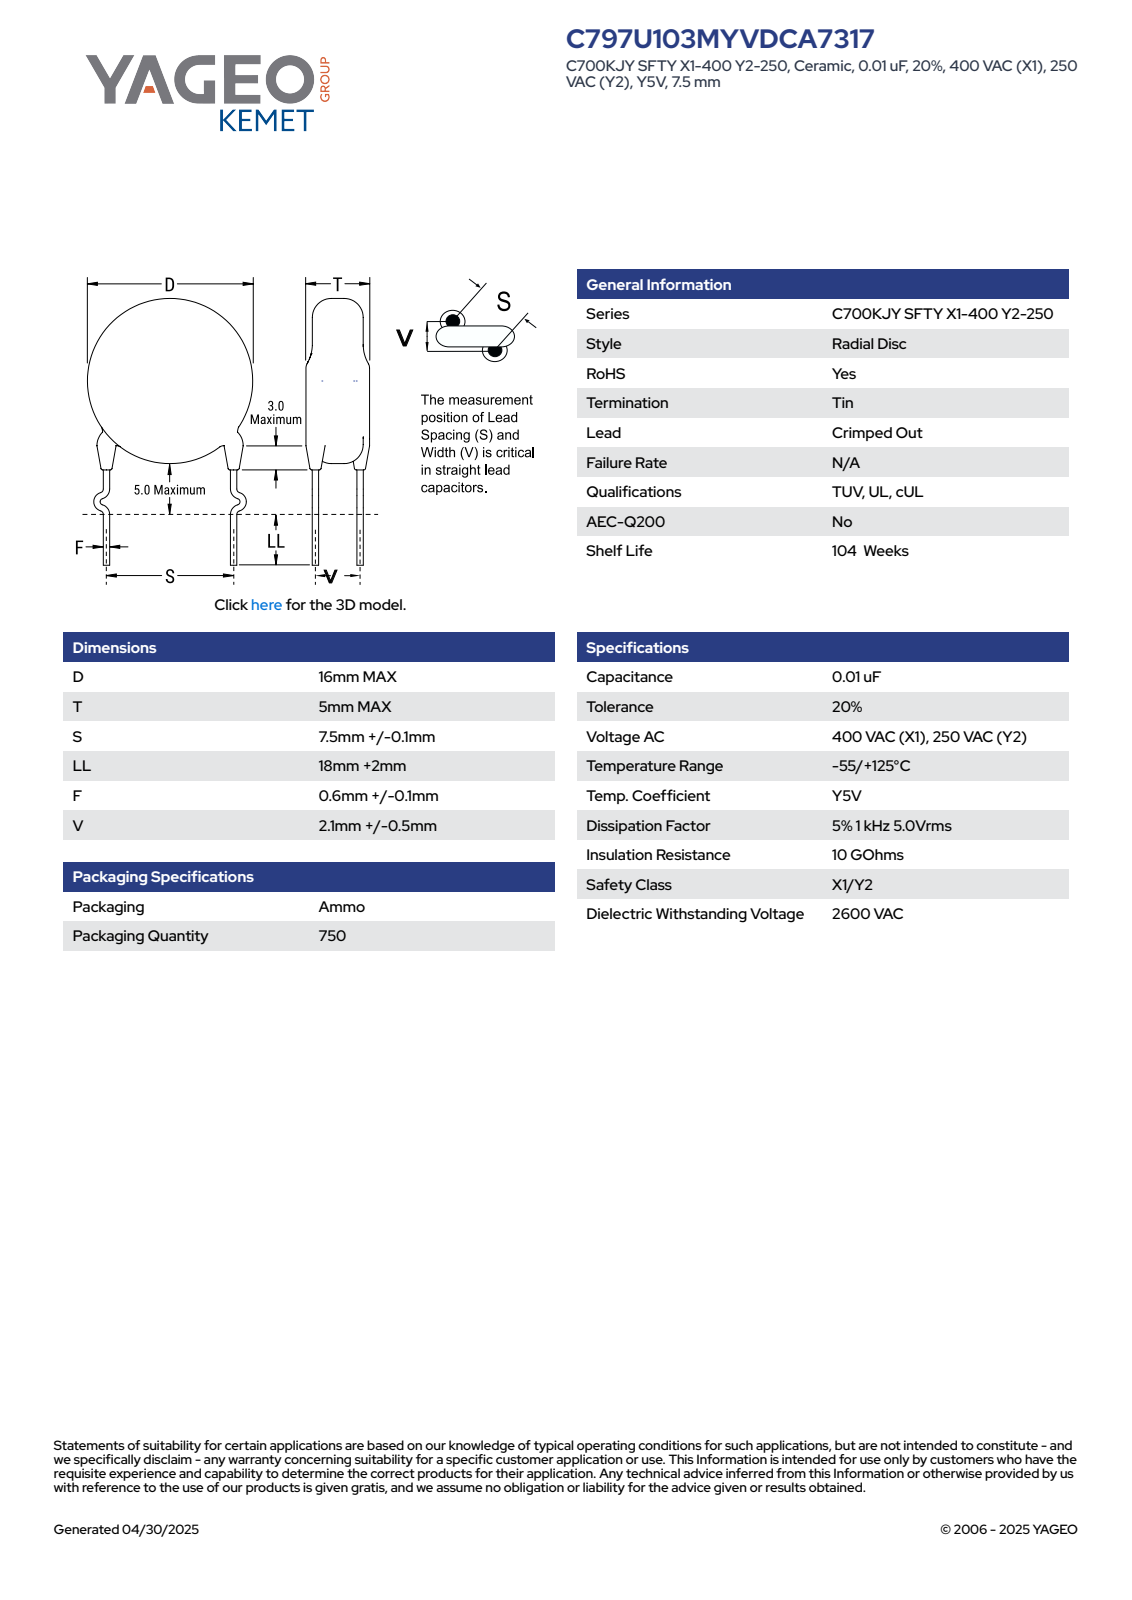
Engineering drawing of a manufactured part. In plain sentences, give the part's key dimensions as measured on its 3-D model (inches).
The part is named "CCD_KCO_16X5_D16T5S7.5LL20F0.7V2.1". Its 3-D file was written by "SolidWorks 2021 (AUTOMOTIVE_DESIGN)". It is 4 solids with 109 faces: 63 planar, 26 cylindrical and 20 other. Overall it measures 1.614 by 0.63 by 0.197 inches. Its volume is 0.061 cubic inches and its surface area 1.17 square inches. Round bosses or shafts: 8 of diameter 0.028, 2 of diameter 0.047, 1 of diameter 0.63. The main face-to-face distances are 0.197, 0.984, 0.074, 1.355, 0.371, 1.281, 0.297, 0.014, 0.059, 0.151.
